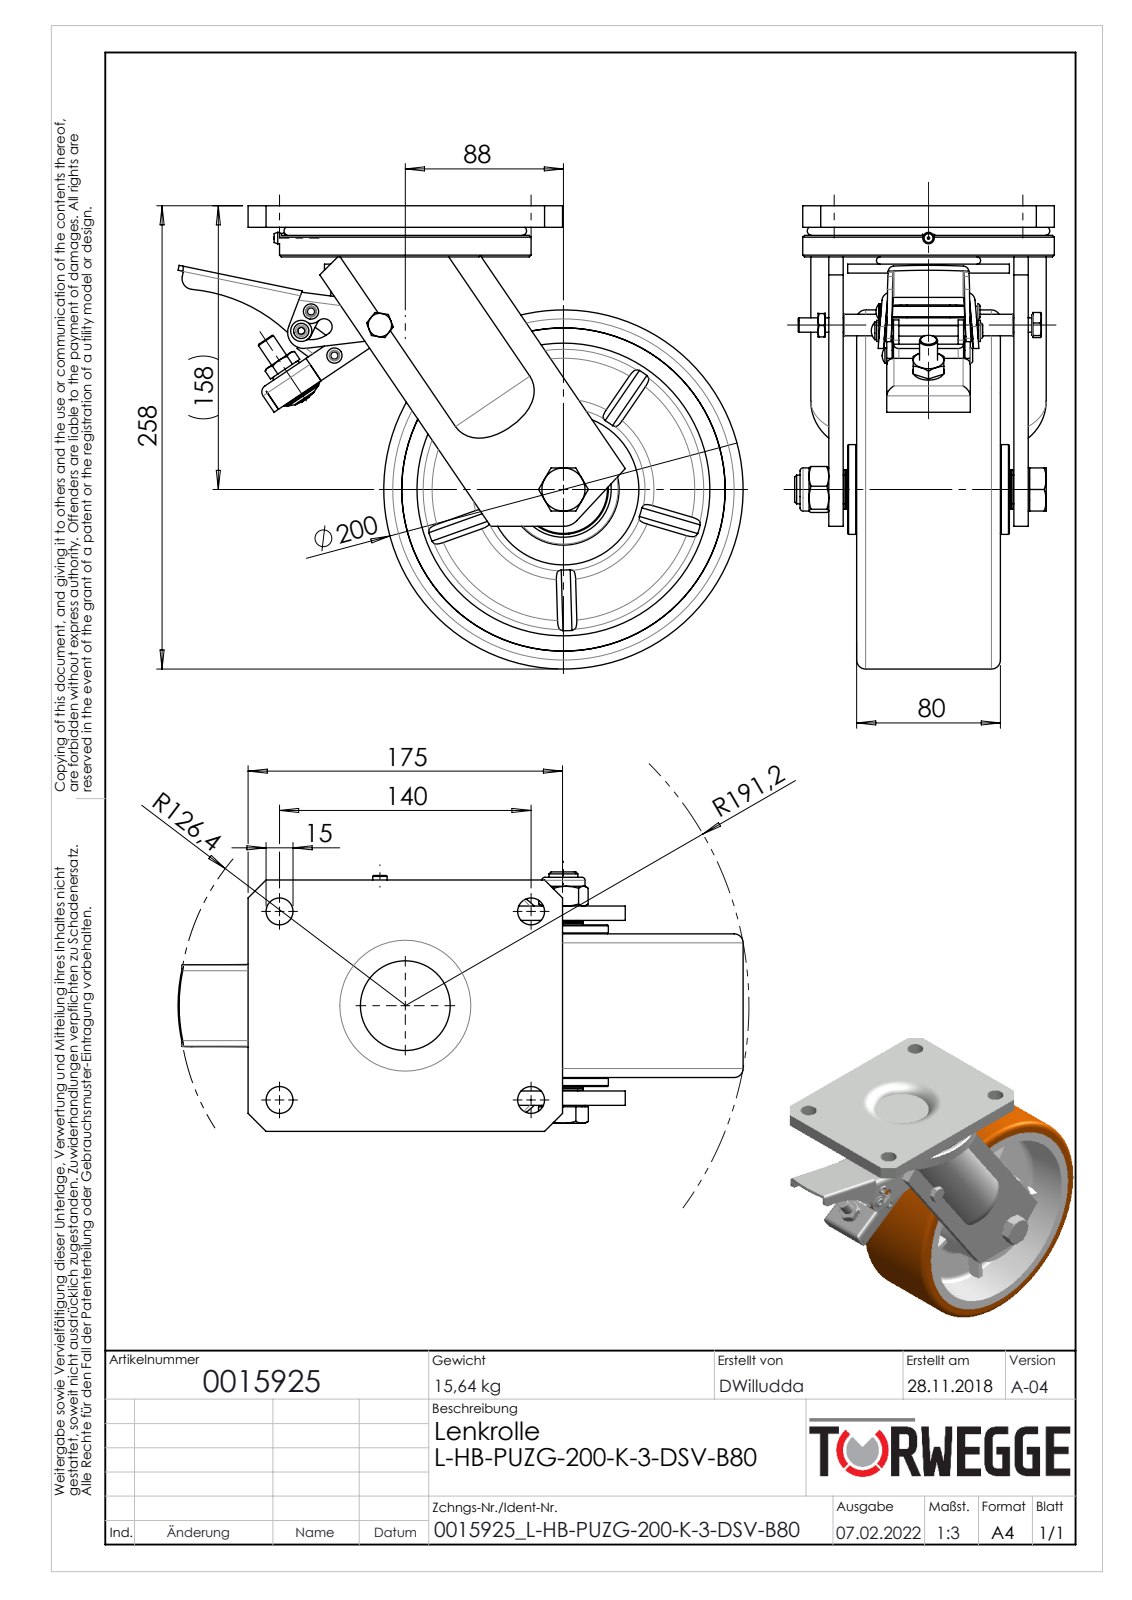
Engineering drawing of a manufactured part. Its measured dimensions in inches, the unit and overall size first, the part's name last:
Units: inches
Overall size (bounding box): 11.482 × 10.039 × 5.689
Round holes (diameter × count): ⌀0.236 ×8, ⌀0.591 ×4, ⌀0.157 ×3, ⌀0.228 ×1, ⌀0.248 ×1, ⌀0.268 ×1, ⌀0.315 ×1, ⌀0.323 ×1, ⌀0.33 ×1, ⌀0.331 ×1, ⌀0.335 ×1, ⌀0.551 ×1
Round bosses / shafts (diameter × count): ⌀0.335 ×3, ⌀0.945 ×2, ⌀0.472 ×2, ⌀0.228 ×2, ⌀7.874 ×1, ⌀5.512 ×1, ⌀5.039 ×1, ⌀3.543 ×1
Partial cylindrical surfaces — rounded edges, fillets, slot ends (radius × count): R0.157 ×5, R0.118 ×4, R0.197 ×4, R0.472 ×4, R0.591 ×4, R0.02 ×3, R0.236 ×3, R0.039 ×2
Main face-to-face distances: 0.472, 1.1, 0.63, 0.628, 1.572, 0.295, 1.457, 1.693, 0.61, 2.067
Hole centre spacings: 3.445, 0.489, 4.134, 5.512, 6.89, 0.476, 0.906, 1.093
Volume: 150.4 in³ · Surface area: 898.2 in²
Bodies: 50 solids, 828 faces (272 planar, 301 cylindrical, 255 other)
Part name (STEP PRODUCT): 0015925
STEP written by: SolidWorks 2020 (AUTOMOTIVE_DESIGN)
